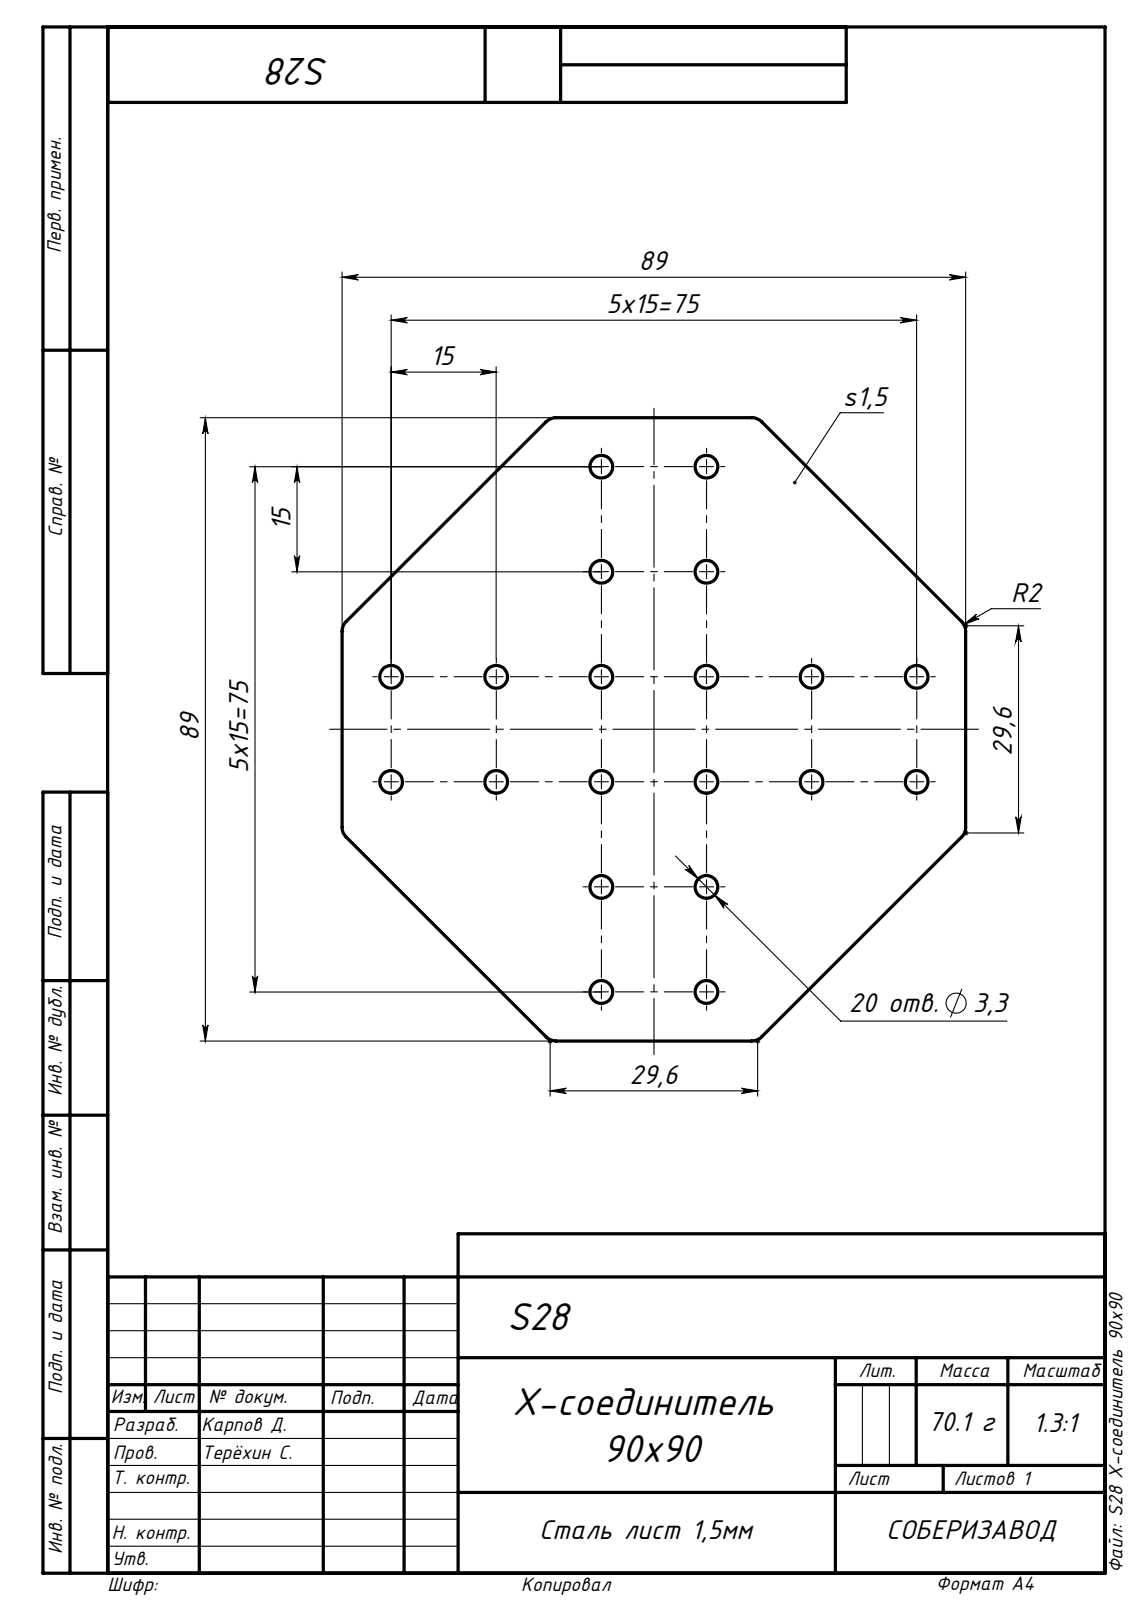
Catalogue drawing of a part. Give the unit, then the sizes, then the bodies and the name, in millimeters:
Units: millimetres
Overall size (bounding box): 89 × 89 × 1.5
Round holes (diameter × count): ⌀3.25 ×20
Partial cylindrical surfaces — rounded edges, fillets, slot ends (radius × count): R2 ×8
Main face-to-face distances: 1.5, 83.84, 89
Hole centre spacings: 33.54, 15, 21.21, 47.43, 30, 42.43, 54.08, 45
Volume: 8 984 mm³ · Surface area: 12 714 mm²
Bodies: 1 solid, 58 faces (10 planar, 48 cylindrical, 0 other)
STEP written by: SolidWorks 2019 (AUTOMOTIVE_DESIGN)
